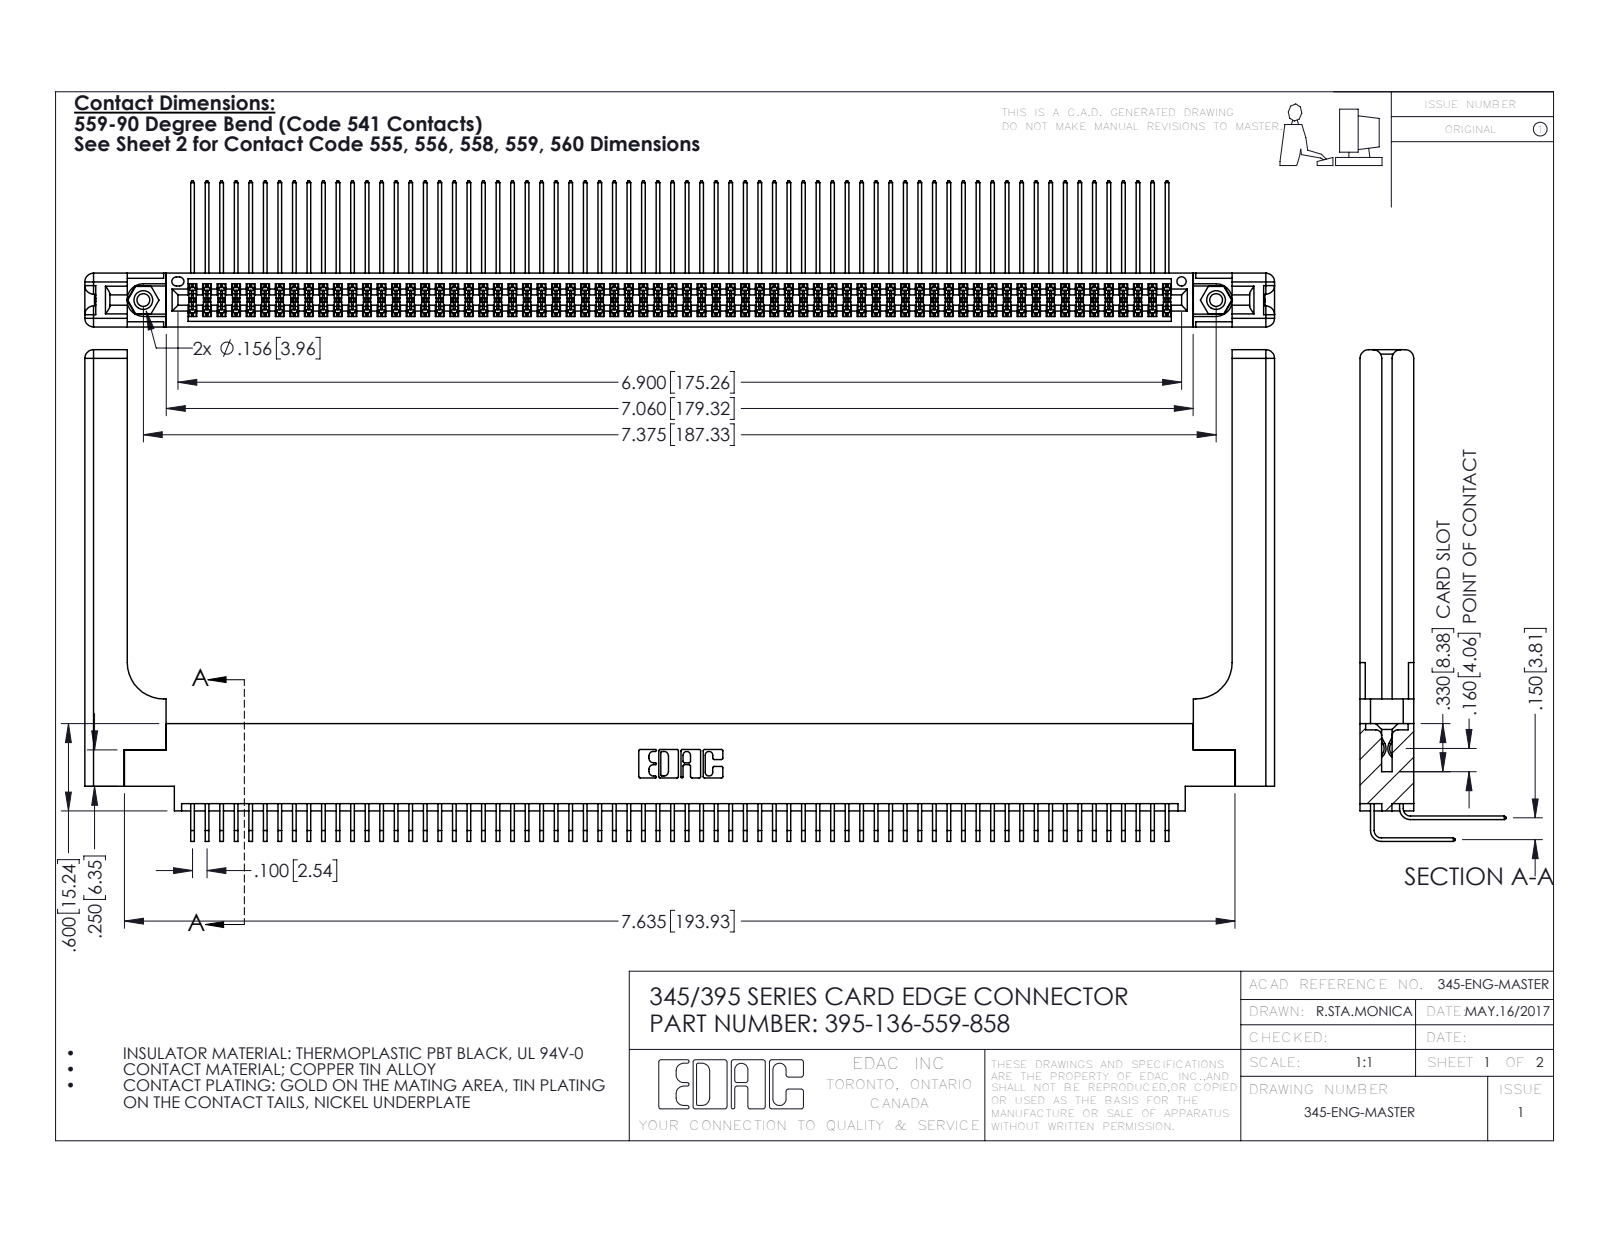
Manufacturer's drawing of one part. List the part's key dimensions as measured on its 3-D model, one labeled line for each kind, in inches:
Part name (STEP PRODUCT): 345 Part_0.170 Offset - 0.156 Dia-TH; 345-220-058_345-220-058; 345-292-001_558 559 Tail - 1; 345-250-001_345-250-001-102 (+2 more)
STEP written by: SolidWorks 2016 (CONFIG_CONTROL_DESIGN)
Units: inches
Bodies: 141 solids, 7458 faces (4992 planar, 2406 cylindrical, 60 other)
Overall size (bounding box): 8.179 × 3.379 × 1.005
Volume: 1.804 in³ · Surface area: 62.89 in²
Round holes (diameter × count): ⌀0.089 ×2, ⌀0.125 ×2, ⌀0.156 ×2, ⌀0.064 ×1
Round bosses / shafts (diameter × count): ⌀0.155 ×2
Partial cylindrical surfaces — rounded edges, fillets, slot ends (radius × count): R0.006 ×272, R0.01 ×22, R0.06 ×16, R0.007 ×6, R0.031 ×6, R0.026 ×3, R0.014 ×2, R0.019 ×2
Main face-to-face distances: 0.072, 0.298, 0.37, 0.098, 0.272, 0.025, 0.2, 0.225, 0.175, 0.15
Hole centre spacings: 0.27, 7.139, 7.375
